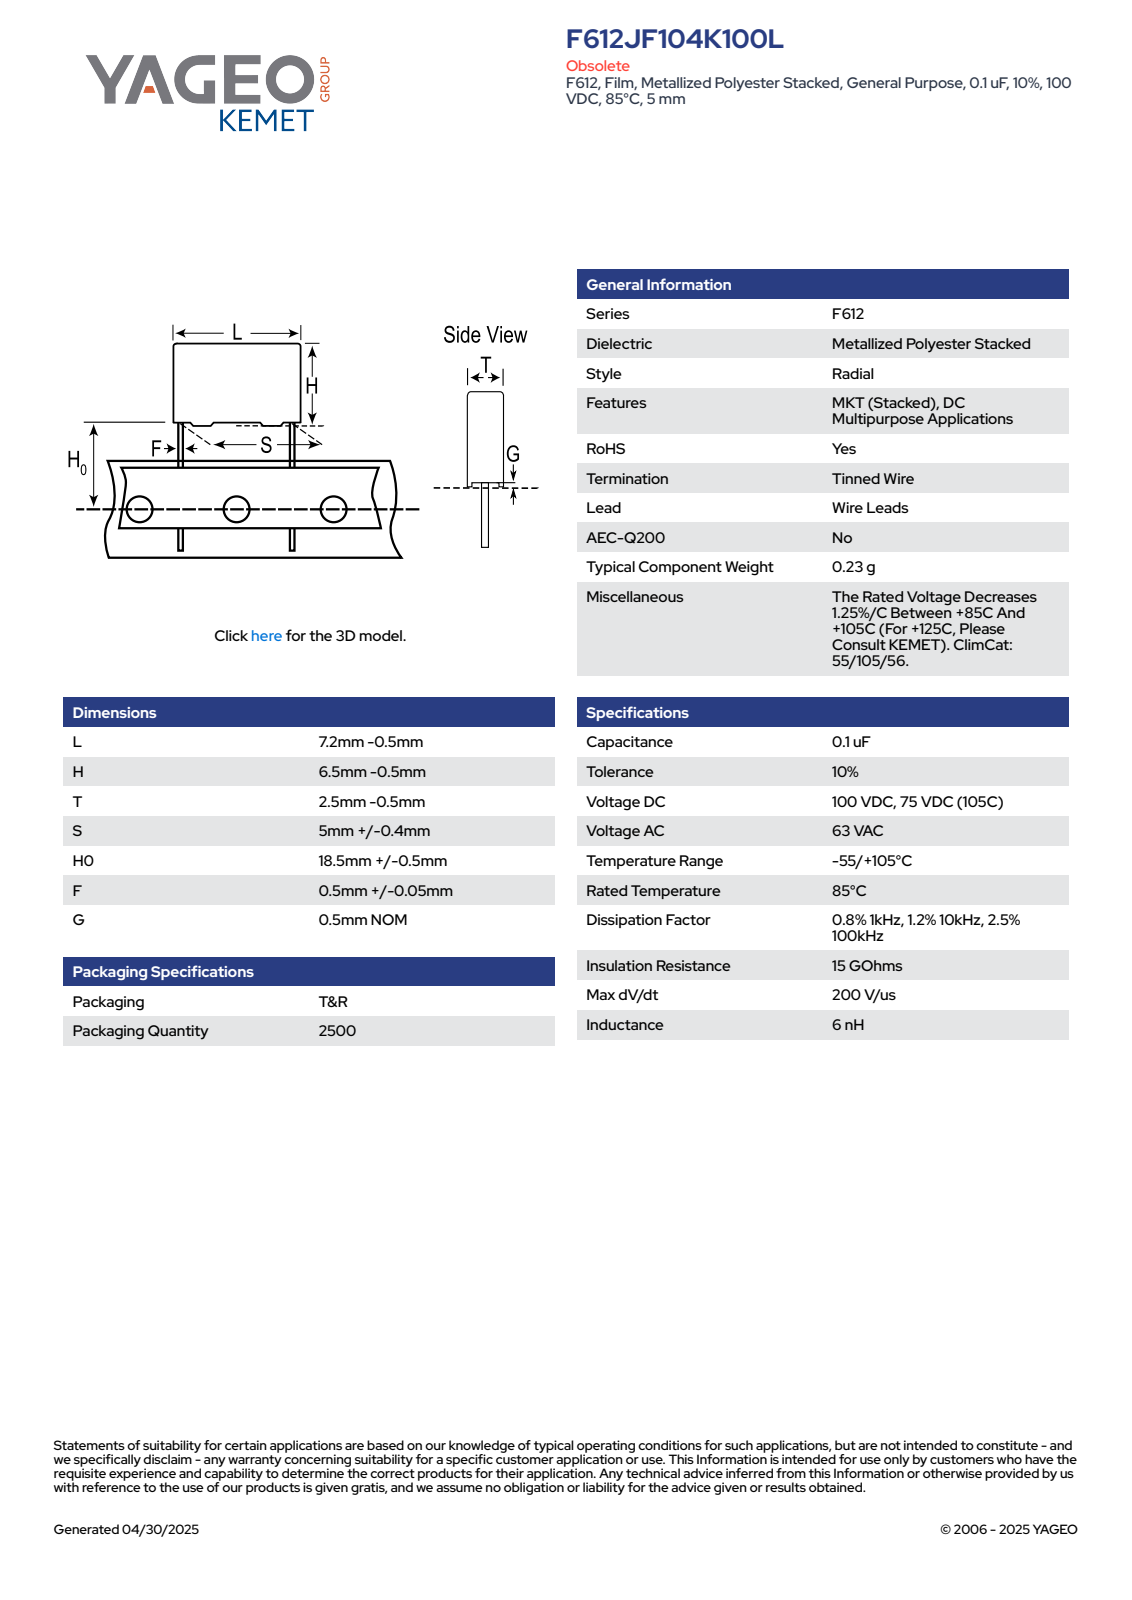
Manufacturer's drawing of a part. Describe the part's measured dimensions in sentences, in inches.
The part is named "CFR_RBG_7.2X6.5X2.5_L6.7H6T2S5H019F0.55G0.5". Its 3-D file was written by "SolidWorks 2014 (AUTOMOTIVE_DESIGN)". It is 4 solids with 89 faces: 81 planar, 8 cylindrical and 0 other. Overall it measures 0.984 by 0.264 by 0.079 inches. Its volume is 0.005 cubic inches and its surface area 0.304 square inches. Round bosses or shafts: 2 of diameter 0.022. Partial cylindrical surfaces (rounded edges, fillets, slot ends): 4 of radius 0.02. The main face-to-face distances are 0.079, 0.264, 0.217, 0.074, 0.07, 0.768, 0.984, 0.748, 0.02, 0.236.
